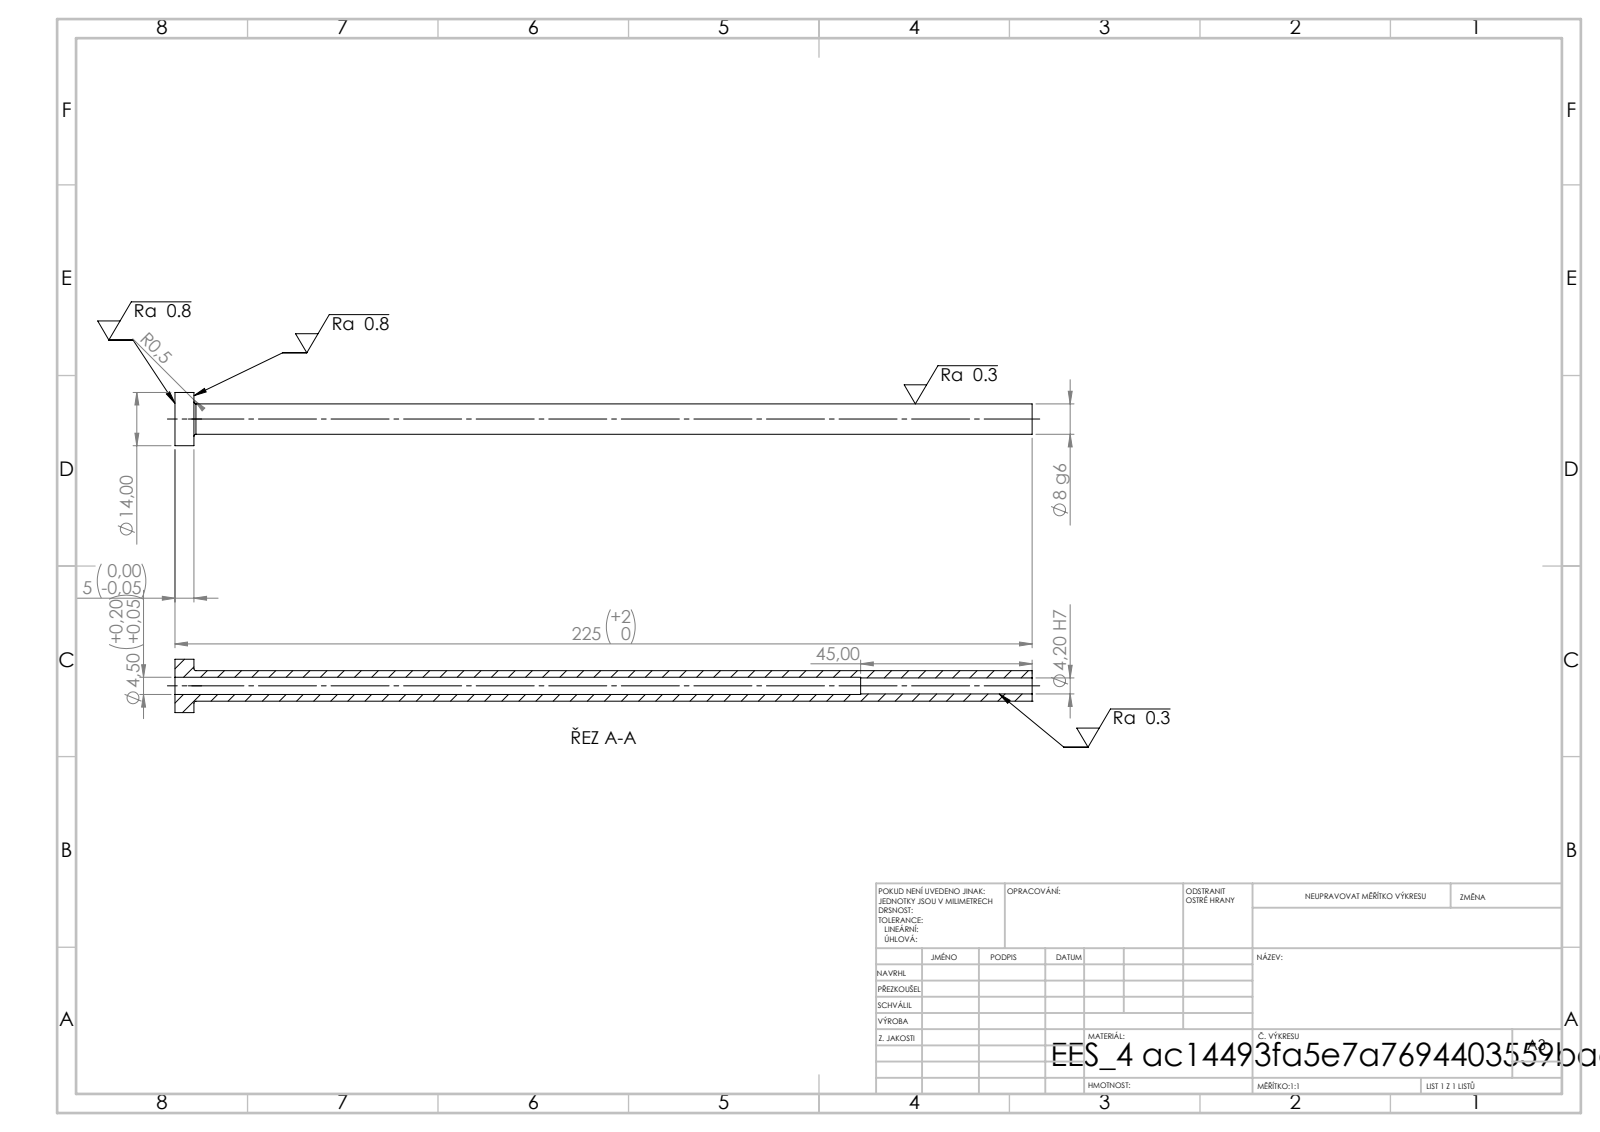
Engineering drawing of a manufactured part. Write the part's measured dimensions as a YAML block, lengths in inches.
step_written_by: "SolidWorks 2019 (CONFIG_CONTROL_DESIGN)"
units: inches
bodies: {solids: 1, faces: 14, planar: 4, cylindrical: 8, other: 2}
overall_size: [8.858, 0.551, 0.551]
volume: 0.509
surface_area: 14.2
round_holes:
  - {diameter: 0.165, count: 1}
  - {diameter: 0.177, count: 1}
round_bosses_or_shafts:
  - {diameter: 0.551, count: 1}
  - {diameter: 0.315, count: 1}
face_to_face_distances: [0.197, 8.858, 8.661, 7.087, 6.89, 1.772]
